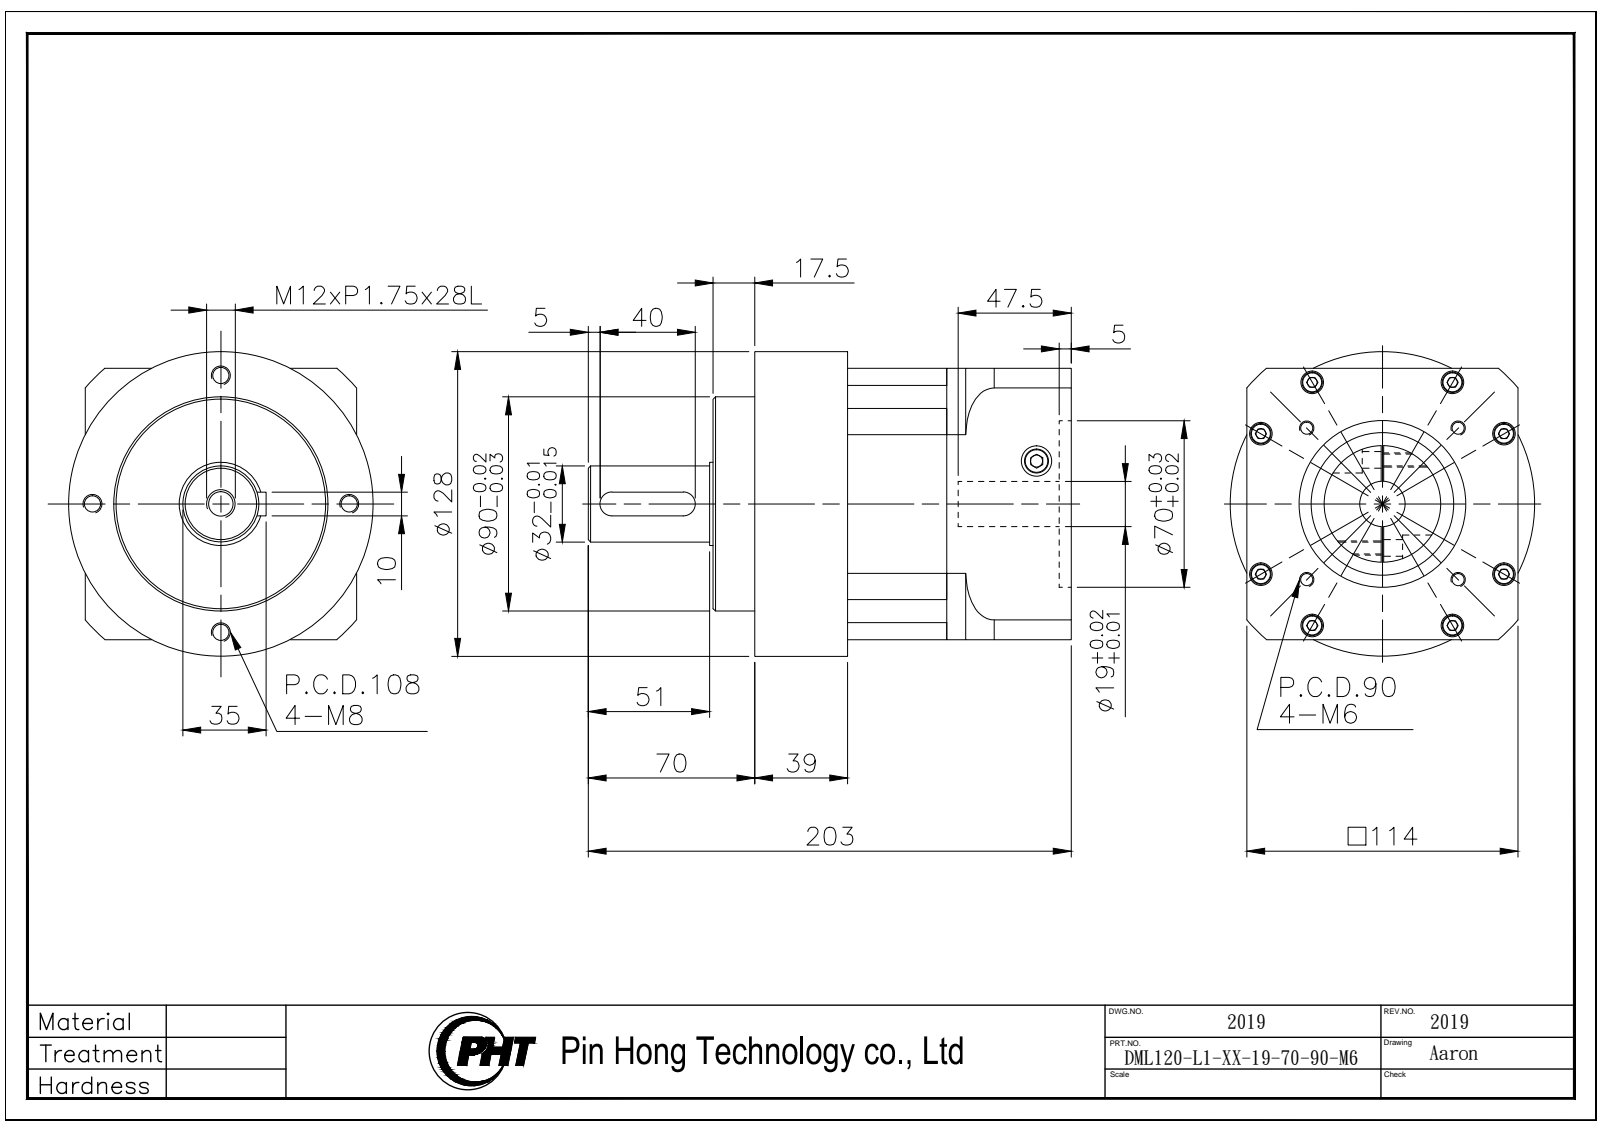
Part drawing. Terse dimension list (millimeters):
name: DML120-L1-XX-19-70-90-M6_2019
written by: SolidWorks 2016 (AUTOMOTIVE_DESIGN)
unit: mm
bodies: 3 solids, 261 faces (108 planar, 113 cylindrical, 40 other)
size: 203 × 128 × 128
volume: 1 688 000 mm³; area: 178 188 mm²
holes: 8× ⌀5.3, 8× ⌀9.5, 4× ⌀5, 4× ⌀6.8, 2× ⌀12.7, 1× ⌀10.2, 1× ⌀19, 1× ⌀60, 1× ⌀70
bosses: 8× ⌀8.5, 1× ⌀128, 1× ⌀90, 1× ⌀49, 1× ⌀35, 1× ⌀32
rounds: 4× R7, 2× R5, 1× R75
face distances: 41.7, 114, 52.3, 94, 56.5, 133, 80.7, 39, 150.5, 98.2
hole spacings: 59, 19.42, 29.64, 38.79, 56.67, 64.28, 82.95, 83.44
